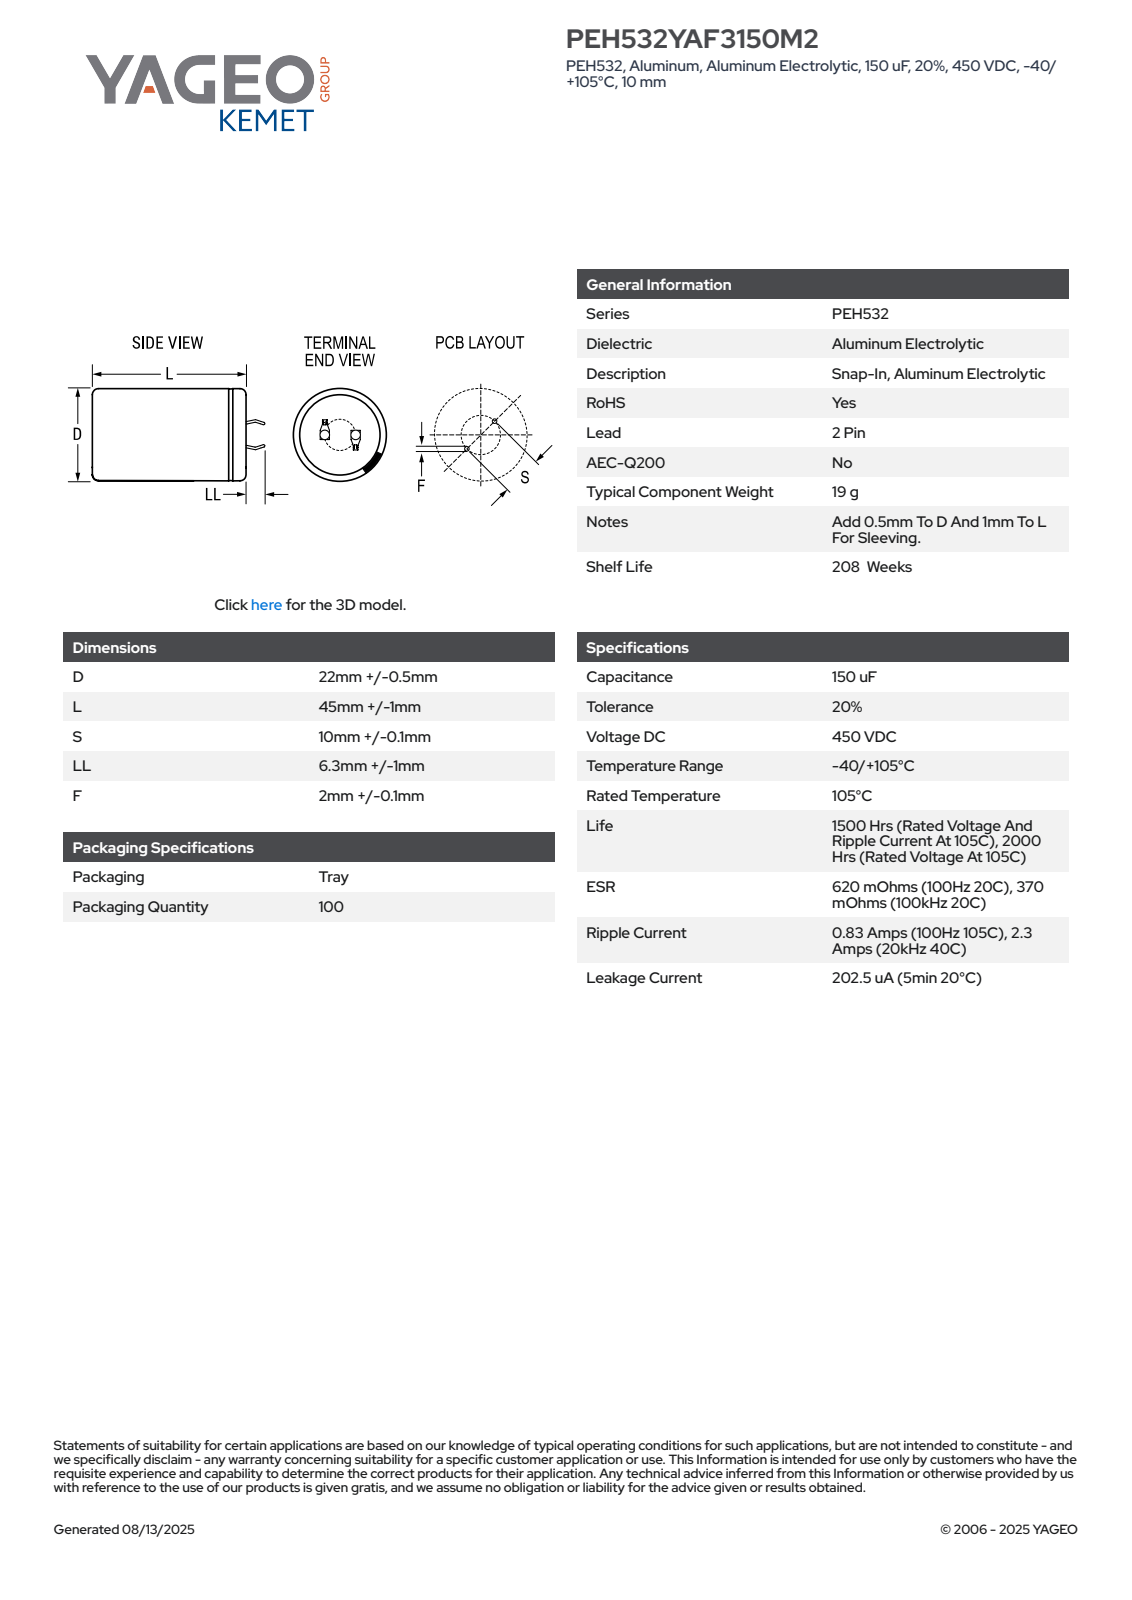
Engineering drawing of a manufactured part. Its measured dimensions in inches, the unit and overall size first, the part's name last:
Units: inches
Overall size (bounding box): 2.098 × 0.886 × 0.886
Round holes (diameter × count): ⌀0.784 ×1
Round bosses / shafts (diameter × count): ⌀0.886 ×1
Partial cylindrical surfaces — rounded edges, fillets, slot ends (radius × count): R0.443 ×1
Main face-to-face distances: 1.811, 0.024, 1.83, 0.02, 0.279, 0.301, 0.03, 0.053, 0.302, 0.255
Volume: 1.109 in³ · Surface area: 6.315 in²
Bodies: 1 solid, 100 faces (52 planar, 9 cylindrical, 39 other)
Part name (STEP PRODUCT): CARS_K2P_22X45_D22.5L46S10LL7.3F2.1
STEP written by: SolidWorks 2014 (AUTOMOTIVE_DESIGN)
